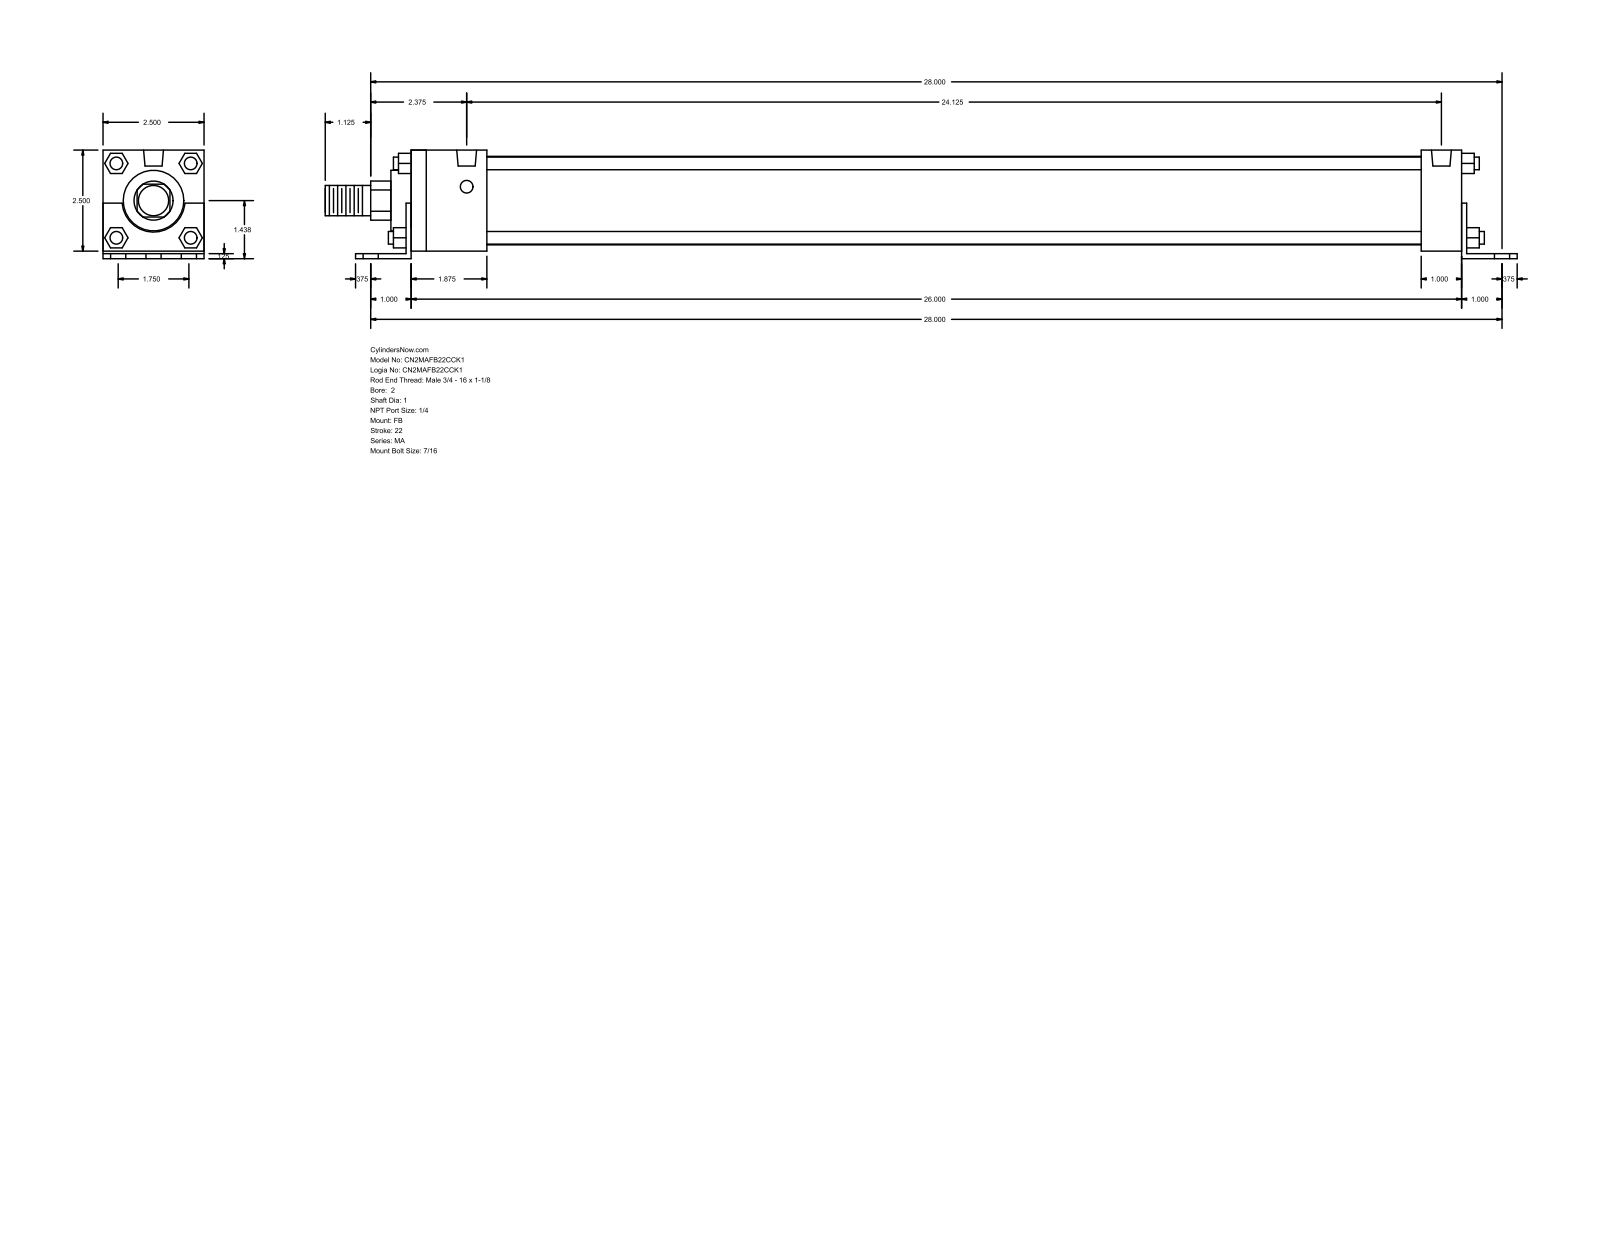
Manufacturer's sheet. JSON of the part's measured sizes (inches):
{"part_name": "MA_FB__0200_1", "step_written_by": "GSSL Pune (CONFIG_CONTROL_DESIGN)", "units": "inches", "bodies": {"solids": 0, "faces": 140, "planar": 105, "cylindrical": 35, "other": 0}, "overall_size": [29.5, 2.687, 2.5], "round_holes": [[0.437, 6], [0.313, 4], [0.492, 2]], "round_bosses_or_shafts": [[0.313, 4], [2.19, 1], [1.5, 1], [1, 1], [0.75, 1]], "partial_cylinders_radius": [[0.484, 1], [0.78, 1]], "face_to_face_distances": [2.5, 0.125, 0.187, 2.687, 0.063, 2.563, 0.5, 0.125, 26, 26.125], "hole_center_spacings": [0.875, 28.014, 28, 1.737, 1.75, 2.531, 24.125, 25.64]}
